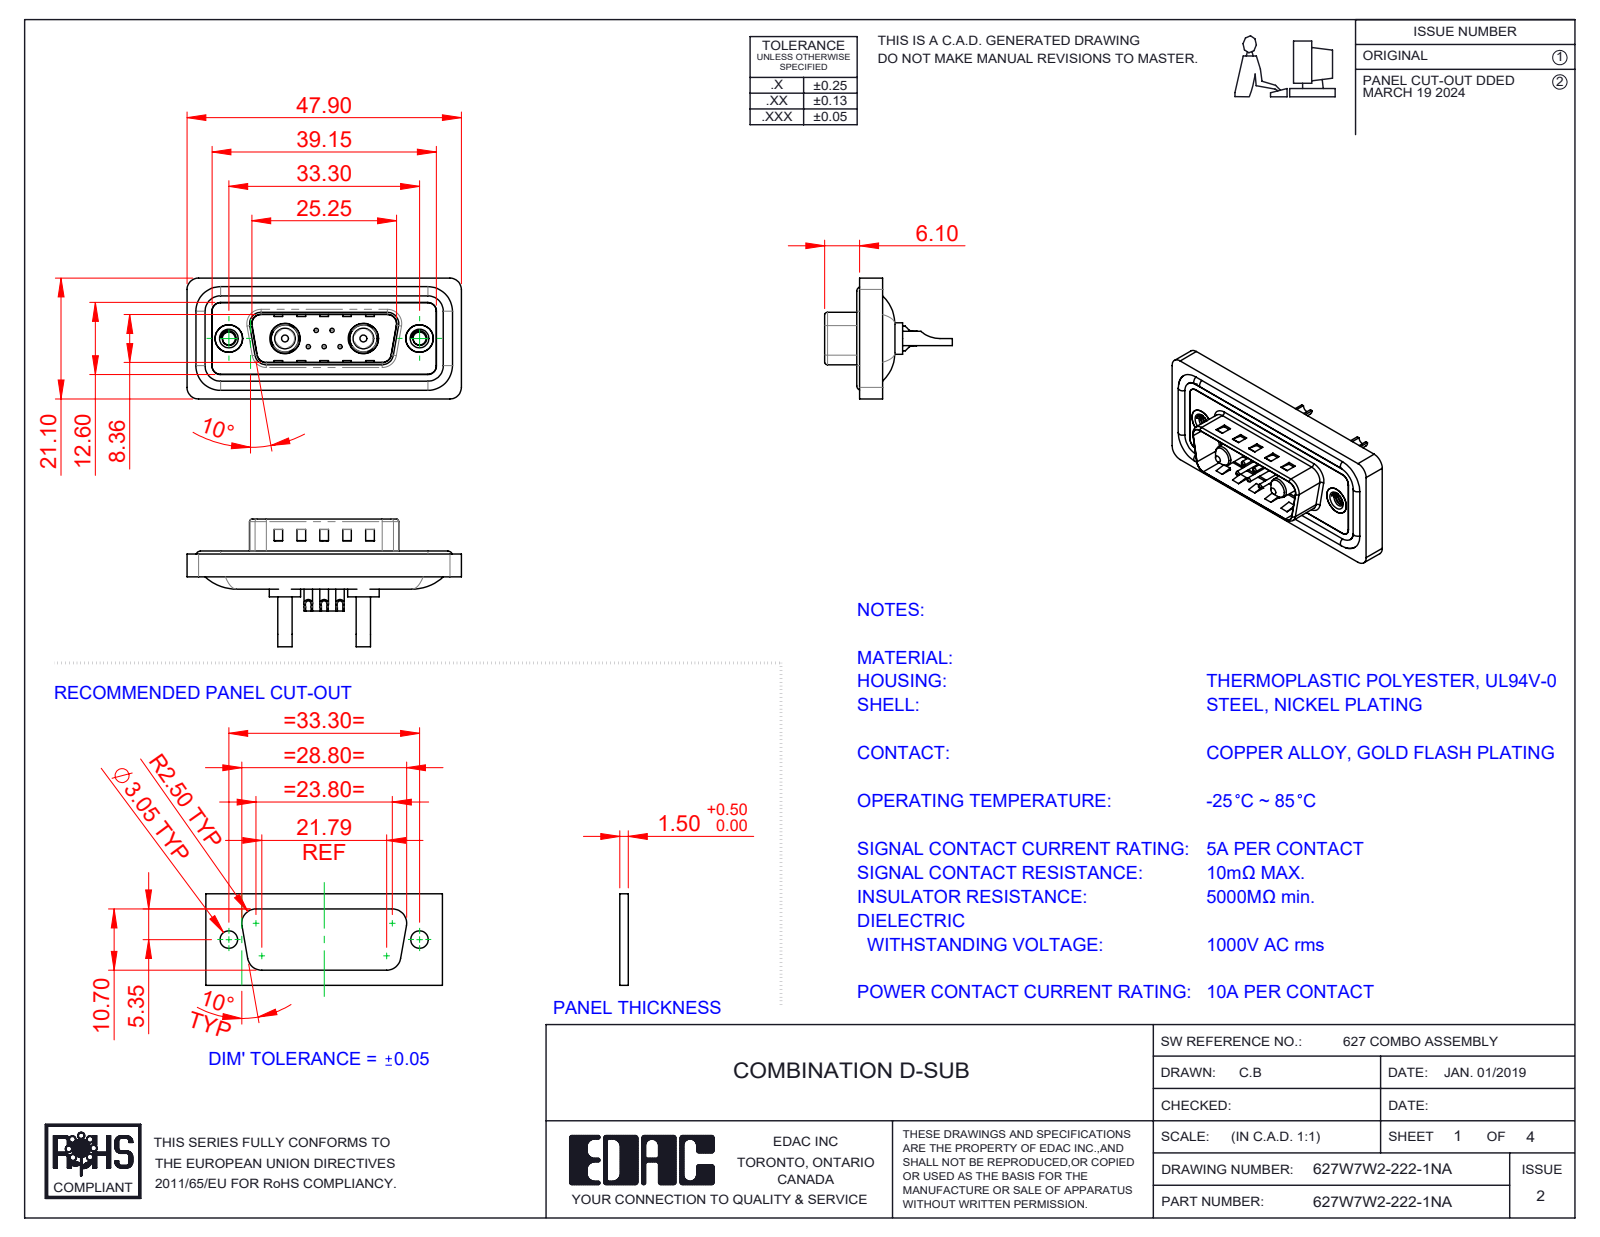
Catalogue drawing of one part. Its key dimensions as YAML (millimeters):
part_name: "627Combo Contact Row 2_22; 627Combo Contact Row 1_22; 627Combo Shell Front_15 Contacts; Power Pin_10A SC (+5 more)"
step_written_by: "SolidWorks 2023 (CONFIG_CONTROL_DESIGN)"
units: millimeters
bodies: {solids: 16, faces: 720, planar: 246, cylindrical: 310, other: 164}
overall_size: [47.9, 22.3, 21.1]
volume: 5521
surface_area: 8926
round_holes:
  - {diameter: 0.75, count: 5}
  - {diameter: 1, count: 5}
  - {diameter: 1.6, count: 5}
  - {diameter: 2, count: 5}
  - {diameter: 1.7, count: 2}
  - {diameter: 2.26, count: 2}
  - {diameter: 4, count: 2}
  - {diameter: 4.8, count: 2}
  - {diameter: 4.85, count: 2}
  - {diameter: 5, count: 2}
  - {diameter: 5.3, count: 2}
round_bosses_or_shafts:
  - {diameter: 1.5, count: 5}
  - {diameter: 1.6, count: 4}
  - {diameter: 5.5, count: 2}
  - {diameter: 5.2, count: 2}
  - {diameter: 4.9, count: 2}
  - {diameter: 4.75, count: 2}
  - {diameter: 3.75, count: 2}
  - {diameter: 3.6, count: 2}
partial_cylinders:
  - {radius: 1.5, count: 26}
  - {radius: 2, count: 20}
  - {radius: 0.5, count: 8}
  - {radius: 1.6, count: 8}
  - {radius: 1, count: 6}
  - {radius: 0.25, count: 4}
  - {radius: 0.6, count: 4}
  - {radius: 0.65, count: 4}
face_to_face_distances: [0.4, 1.1, 1.5, 1.6, 0.5, 3.1, 2.9, 4, 0.82, 9.58]
hole_center_spacings: [3.16, 2.77, 9.8, 23.5, 4.31, 4.33, 5.03, 5.04]
